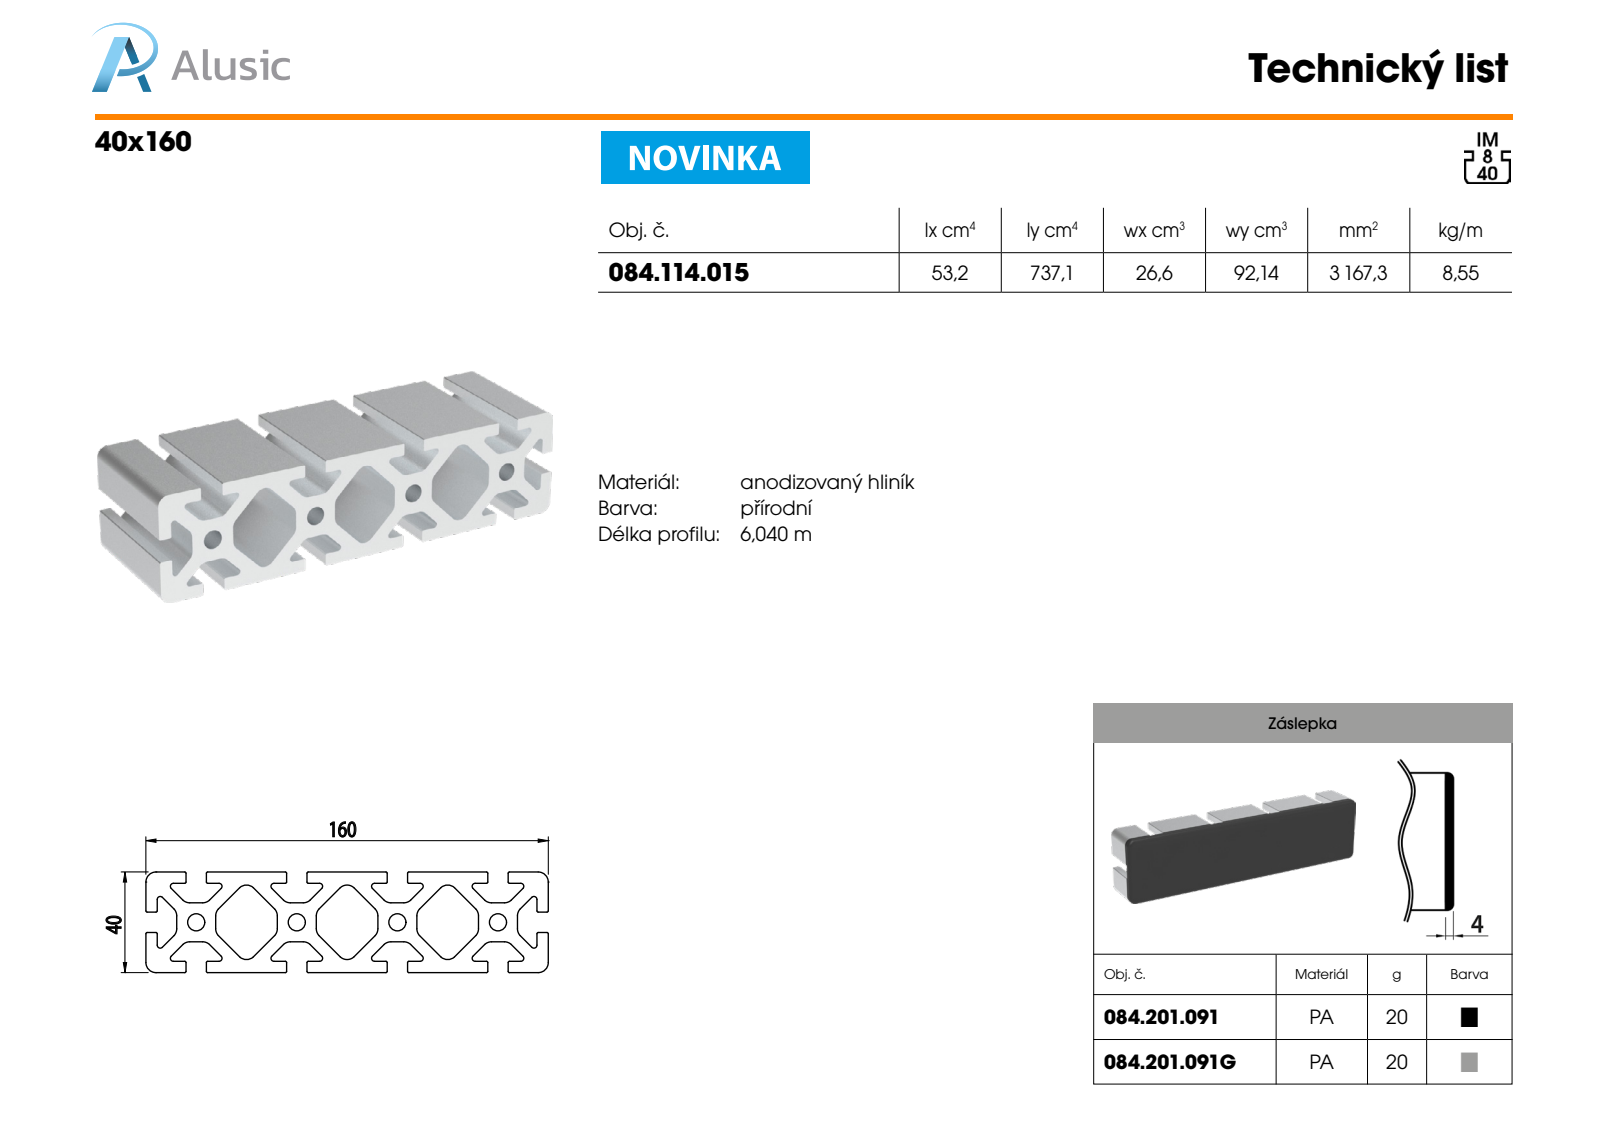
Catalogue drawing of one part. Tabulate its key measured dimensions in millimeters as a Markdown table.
| quantity | value |
| --- | --- |
| part name | 084.114.015 |
| STEP written by | SolidWorks 2018 (AUTOMOTIVE_DESIGN) |
| units | millimeters |
| bodies | 1 solid, 219 faces (104 planar, 115 cylindrical, 0 other) |
| overall size | 160 × 100 × 40 |
| volume | 316 733 mm³ |
| surface area | 118 763 mm² |
| round holes (diameter × count) | 6.8 × 4 |
| partial cylindrical surfaces (radius × count) | 4 × 42, 0.5 × 40, 1.2 × 20 |
| main face-to-face distances | 28.28, 40, 56.56, 5, 23.28, 33.28, 4.5, 51.56, 35.5, 3.7 |
| hole center spacings | 40, 80, 120 |
